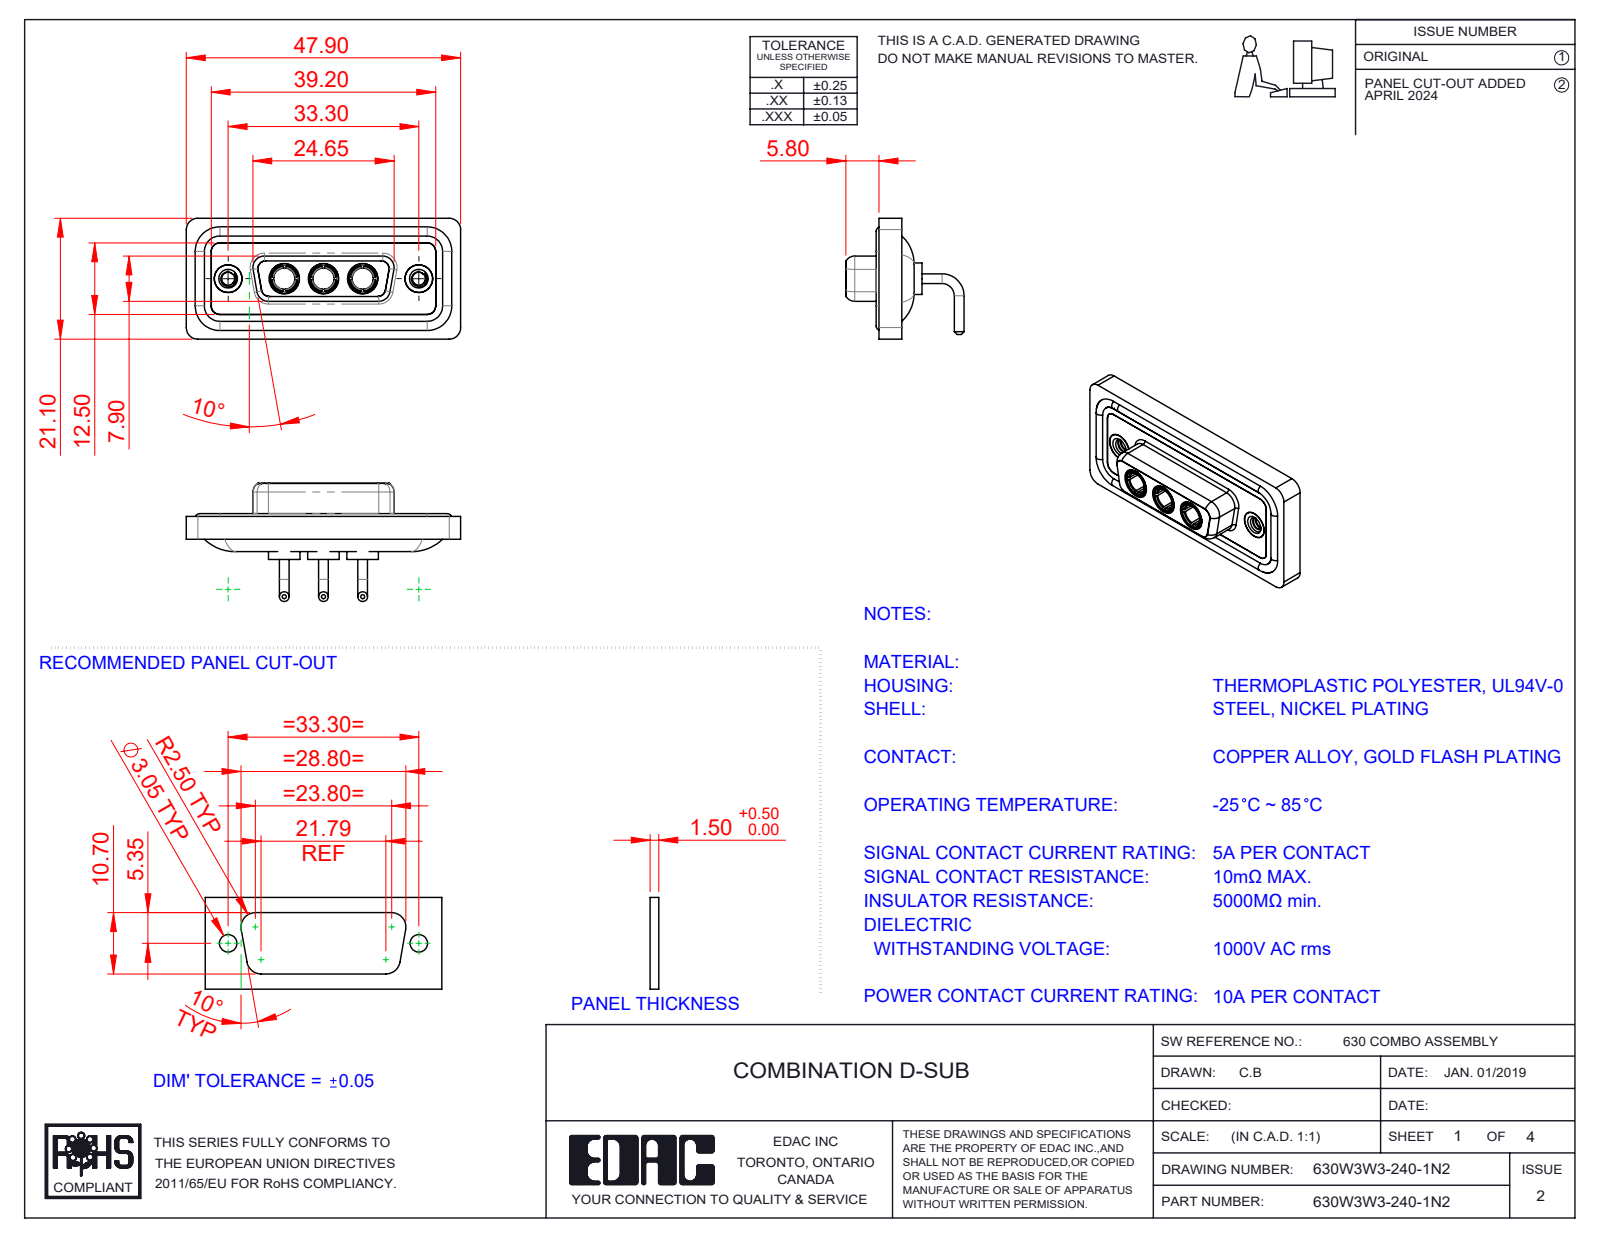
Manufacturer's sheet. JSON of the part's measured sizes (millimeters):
{"part_name": "630W3W3-140-1N2; 630Combo Housing_3W3; 630Combo Waterproof Housing_15 Contacts; 630Combo Shell Rear_15 Contacts (+3 more)", "step_written_by": "SolidWorks 2023 (CONFIG_CONTROL_DESIGN)", "units": "millimeters", "bodies": {"solids": 13, "faces": 620, "planar": 192, "cylindrical": 263, "other": 165}, "overall_size": [47.9, 21.1, 20.65], "volume_mm3": 6006, "surface_area_mm2": 9819, "round_holes": [[4.85, 5], [3.7, 3], [5.3, 3], [2.26, 2], [4, 2], [4.05, 2], [5, 2]], "round_bosses_or_shafts": [[1.7, 6], [1.6, 4], [5.5, 3], [5.2, 3], [4.96, 3], [4.75, 3], [3.75, 3], [4.95, 2]], "partial_cylinders_radius": [[2, 20], [1.5, 18], [1.35, 12], [1.6, 8], [0.25, 4], [0.5, 4], [0.6, 4], [0.65, 4]], "face_to_face_distances": [0.4, 1.8, 1.1, 1.6, 2.9, 2.5, 3.1, 3.7, 1.5, 4.1], "hole_center_spacings": [6.85, 9.8, 16.65, 23.5, 13.7, 33.3]}
